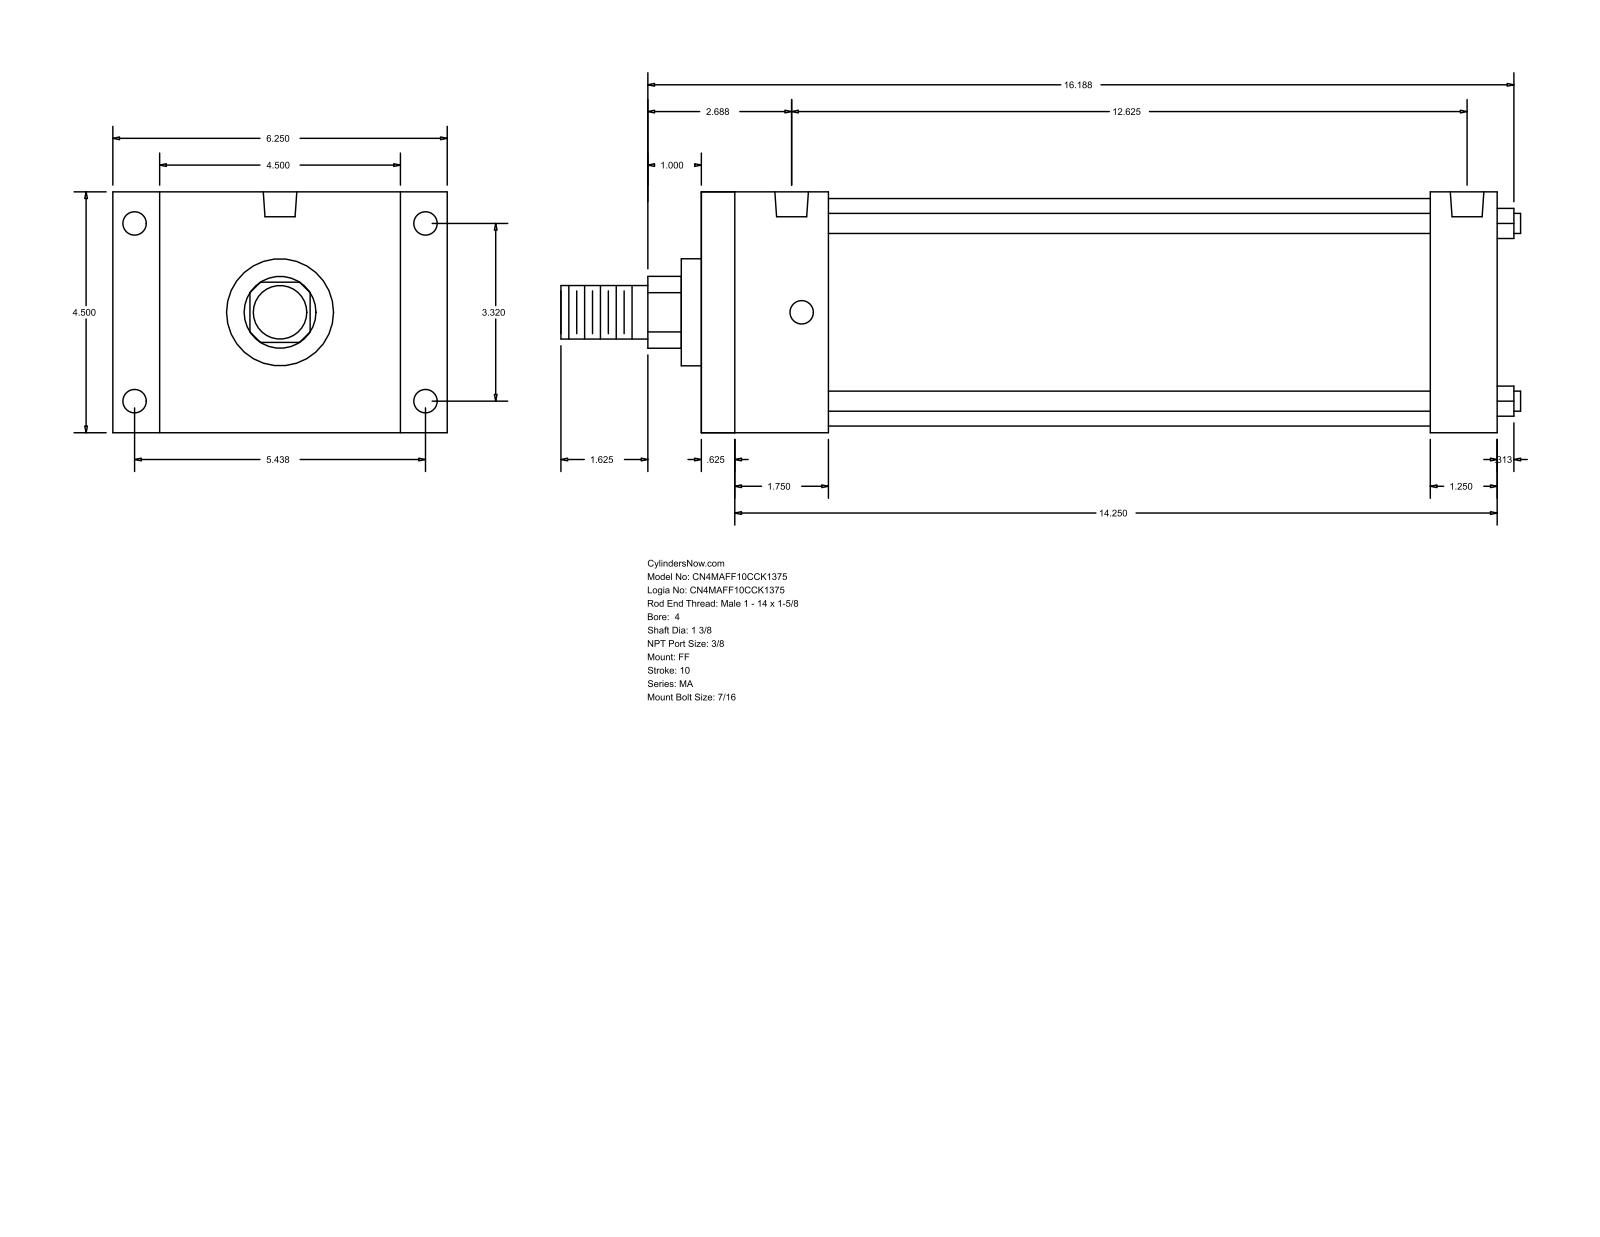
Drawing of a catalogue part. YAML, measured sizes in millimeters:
part_name: "MA_FF__0400_1.375"
step_written_by: "GSSL Pune (CONFIG_CONTROL_DESIGN)"
units: millimeters
bodies: {solids: 0, faces: 92, planar: 64, cylindrical: 28, other: 0}
overall_size: [455.61, 158.75, 114.3]
round_holes:
  - {diameter: 11.11, count: 8}
  - {diameter: 15.93, count: 2}
round_bosses_or_shafts:
  - {diameter: 9.53, count: 4}
  - {diameter: 107.95, count: 1}
  - {diameter: 50.8, count: 1}
  - {diameter: 34.92, count: 1}
  - {diameter: 25.4, count: 1}
partial_cylinders:
  - {radius: 17.06, count: 1}
face_to_face_distances: [114.3, 377.83, 15.87, 361.96, 22.23, 136.53, 346.08, 330.21, 31.75, 60.32]
hole_center_spacings: [84.32, 138.12, 161.82, 311.15, 4.76, 4.77, 315.91, 315.92]
